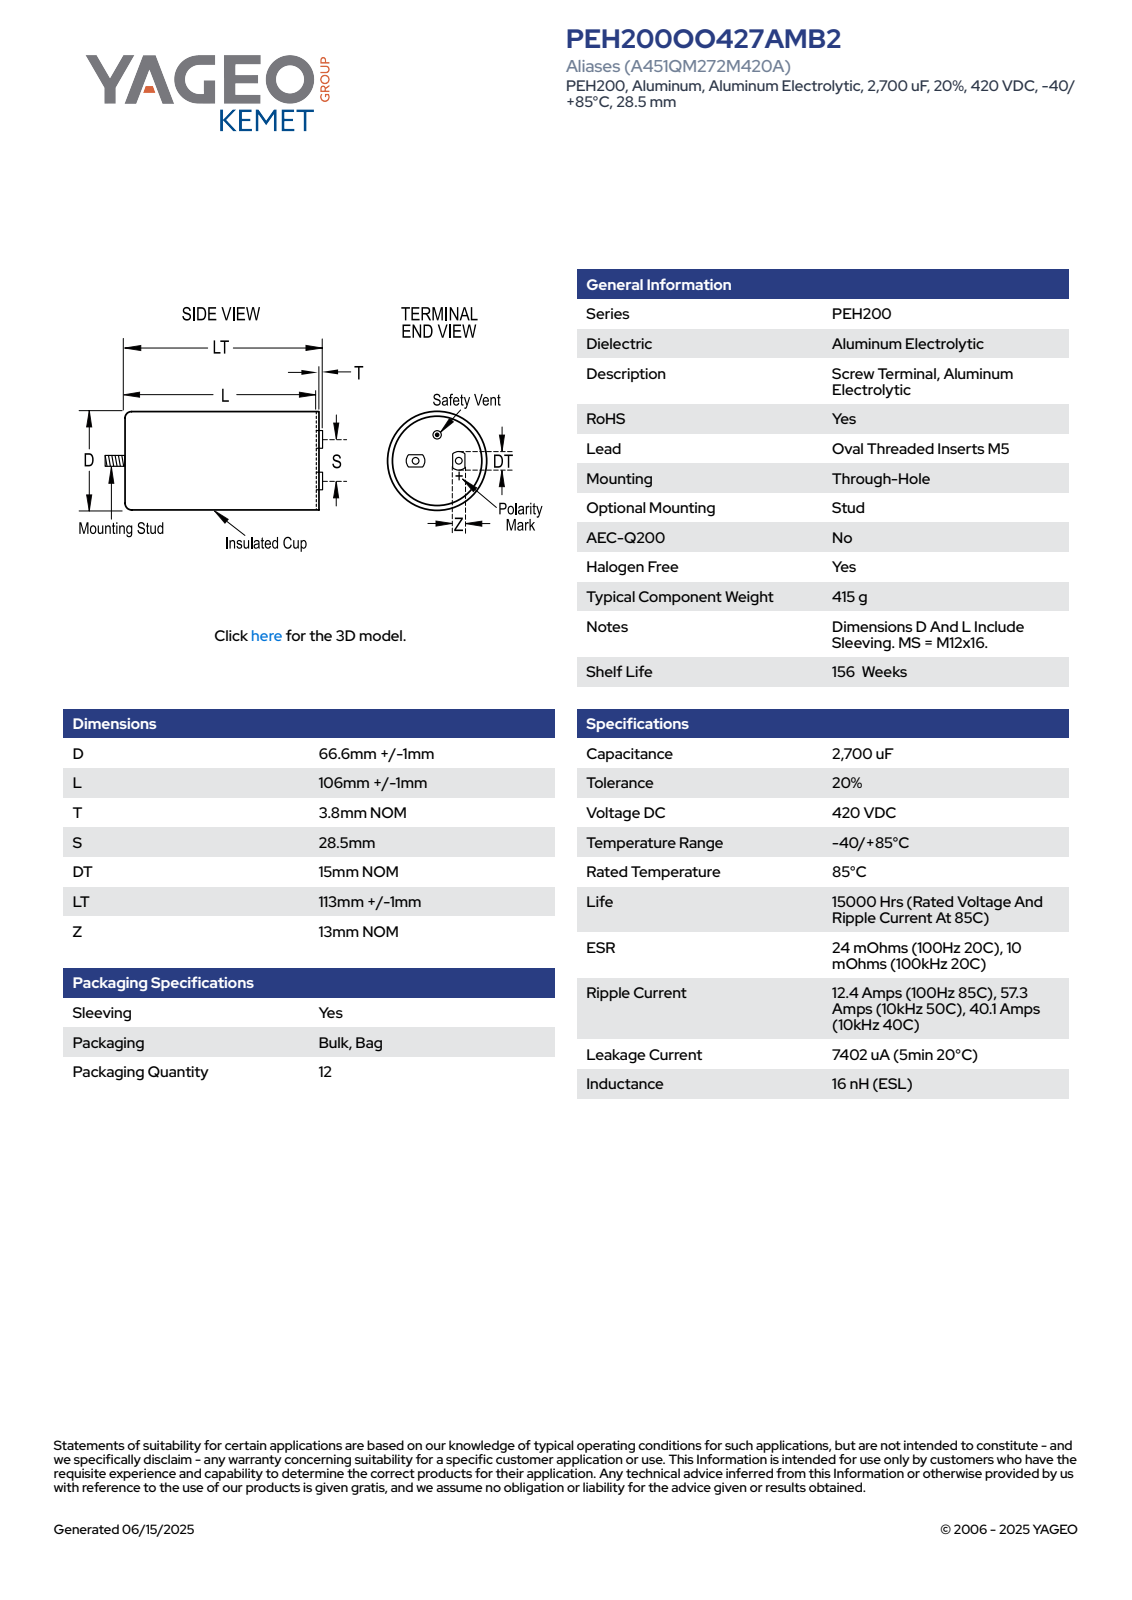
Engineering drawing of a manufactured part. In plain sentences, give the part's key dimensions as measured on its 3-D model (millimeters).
The part is named "Stud; Can_19; CARCS_D67.6L107S28.5T3.8; Oval_Terminal_19". Its 3-D file was written by "SolidWorks 2014 (AUTOMOTIVE_DESIGN)". It is 4 solids with 185 faces: 70 planar, 83 cylindrical and 32 other. Overall it measures 130 by 67.6 by 67.6 millimeters. Its volume is 388 321 cubic millimeters and its surface area 33 699 square millimeters. Round holes: 2 of diameter 4.02, 1 of diameter 65.6. Round bosses or shafts: 2 of diameter 7.5, 1 of diameter 67.6, 1 of diameter 12, 1 of diameter 11.6. Partial cylindrical surfaces (rounded edges, fillets, slot ends): 2 of radius 7.5, 1 of radius 33.79. The main face-to-face distances are 107, 7, 114, 3.2, 3.8, 110.2, 5, 130, 126.2, 123. The hole center spacings are 14.25, 28.5.
